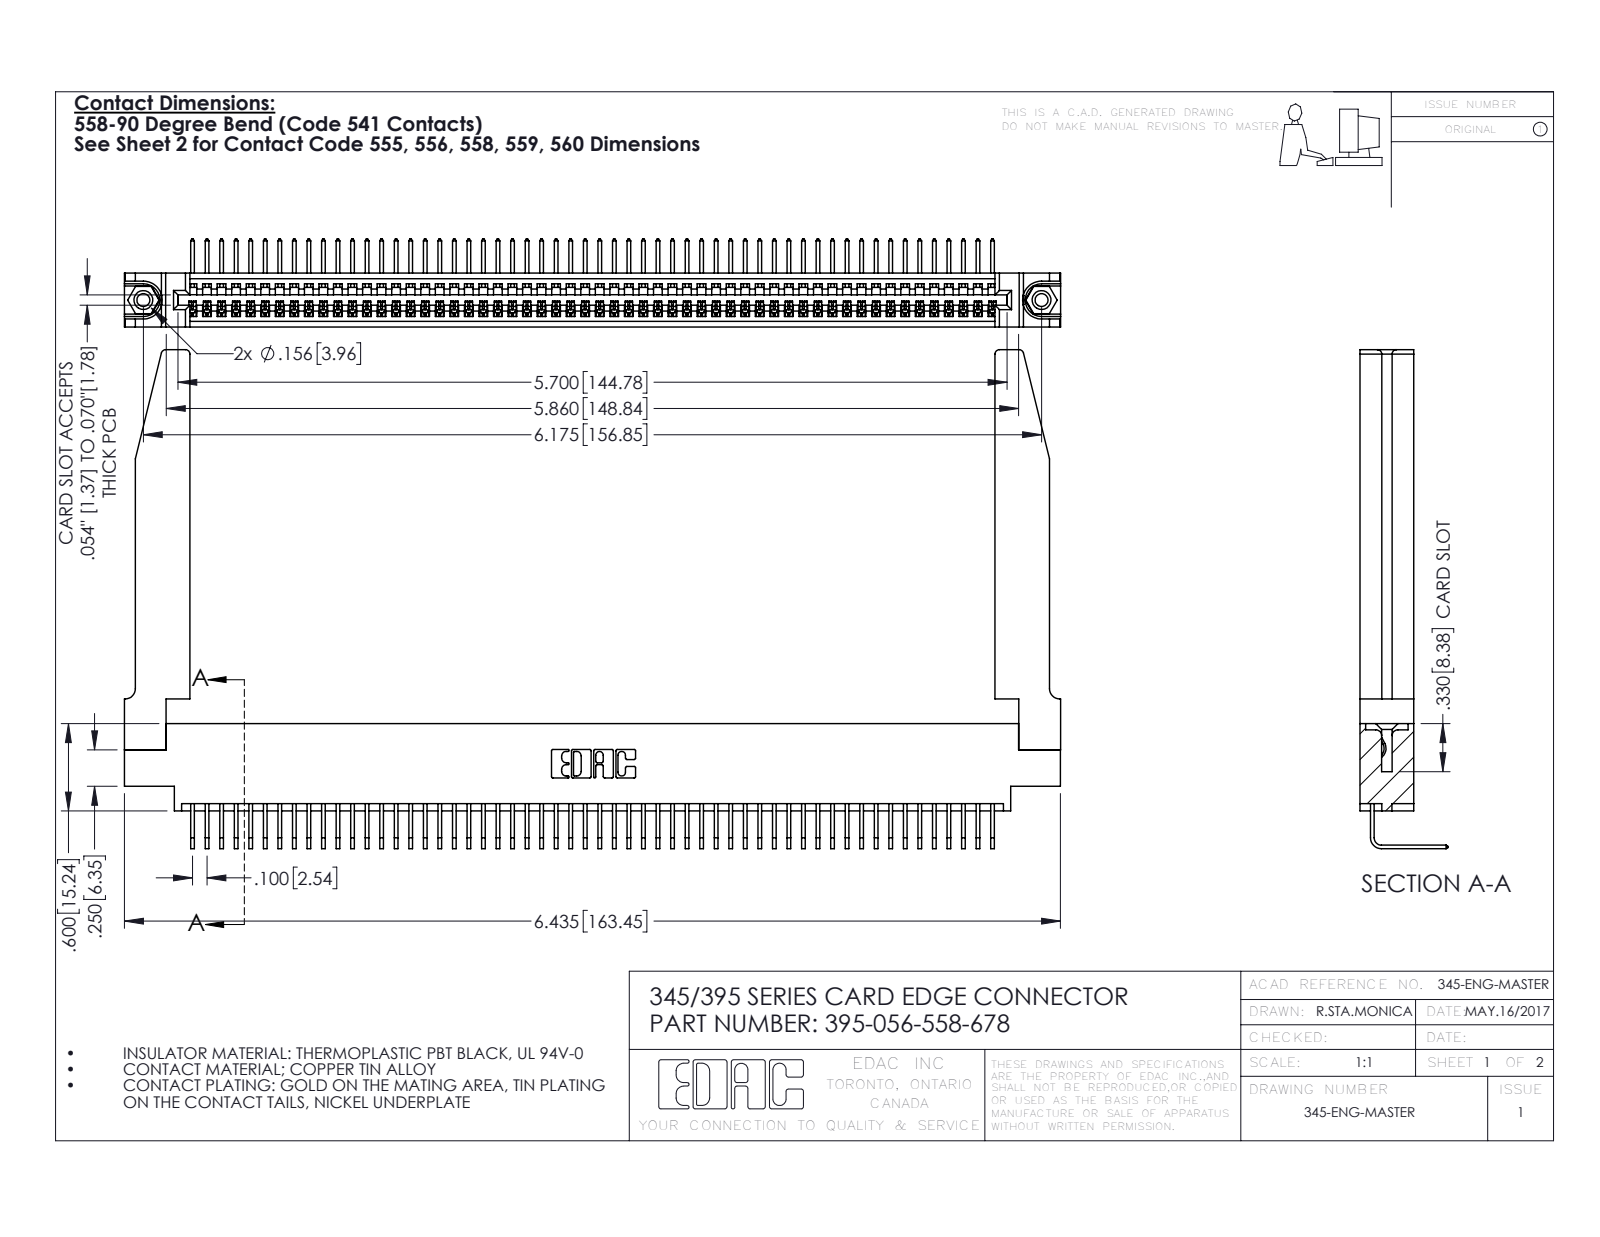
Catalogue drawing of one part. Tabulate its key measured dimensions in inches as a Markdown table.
| quantity | value |
| --- | --- |
| part name | 345-250-001_345-250-001-102; 395-056-558-678; 345-292-001_558 Tail - 2; 345 Part_0.170 Offset - 0.156 Dia-TH (+1 more) |
| STEP written by | SolidWorks 2016 (CONFIG_CONTROL_DESIGN) |
| units | inches |
| bodies | 61 solids, 3724 faces (2578 planar, 1094 cylindrical, 52 other) |
| overall size | 6.436 × 3.429 × 0.605 |
| volume | 1.433 in³ |
| surface area | 45.17 in² |
| round holes (diameter × count) | 0.089 × 2, 0.125 × 2, 0.156 × 2, 0.064 × 1 |
| round bosses / shafts (diameter × count) | 0.155 × 2 |
| partial cylindrical surfaces (radius × count) | 0.006 × 112, 0.01 × 22, 0.03 × 8, 0.007 × 6, 0.031 × 6, 0.026 × 3, 0.031 × 2, 0.04 × 2 |
| main face-to-face distances | 0.37, 0.072, 0.298, 0.098, 0.272, 0.025, 0.2, 0.225, 0.148, 0.15 |
| hole center spacings | 0.27, 5.939, 6.175 |
